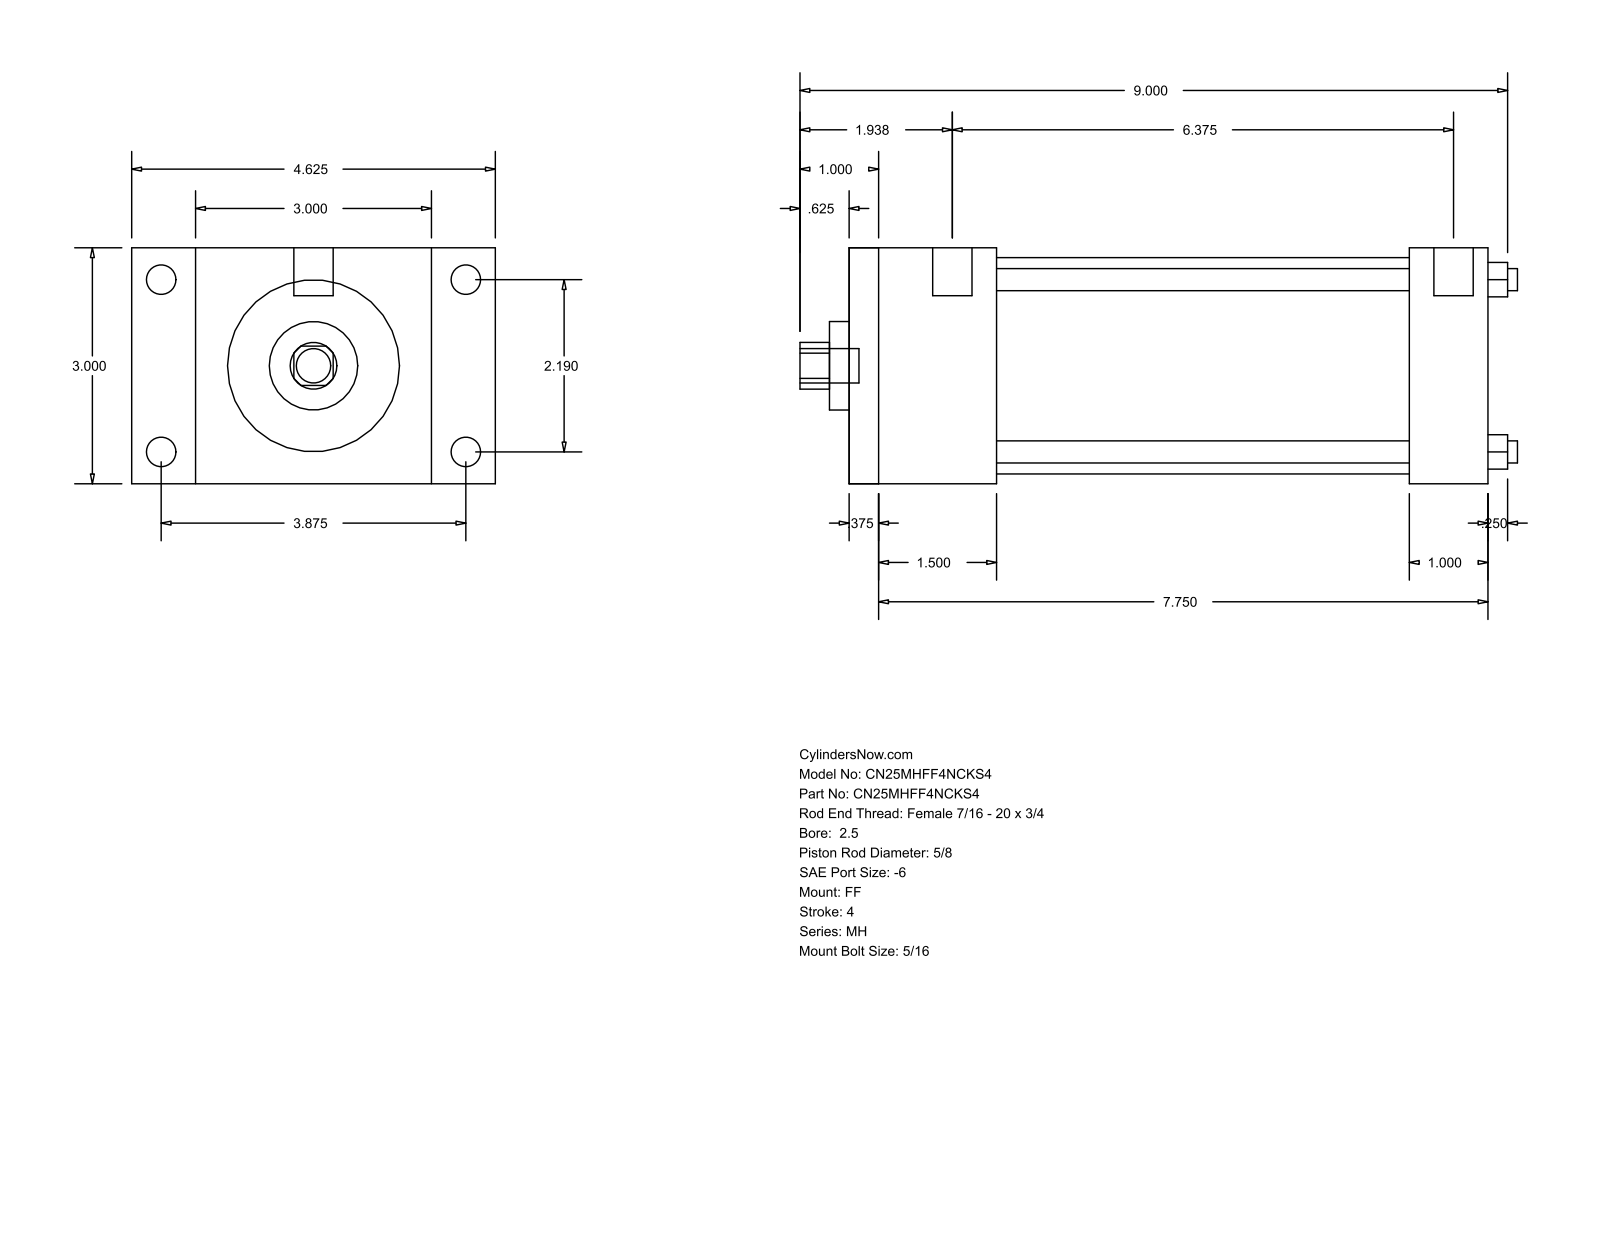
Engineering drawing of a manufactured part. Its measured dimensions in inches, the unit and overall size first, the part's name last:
Units: inches
Overall size (bounding box): 9.125 × 4.625 × 3
Round holes (diameter × count): ⌀0.281 ×4, ⌀0.625 ×1, ⌀1.125 ×1, ⌀2.75 ×1
Round bosses / shafts (diameter × count): ⌀0.375 ×4, ⌀0.219 ×4, ⌀0.5 ×2, ⌀0.437 ×1
Partial cylindrical surfaces — rounded edges, fillets, slot ends (radius × count): R0.297 ×1
Main face-to-face distances: 3, 8.125, 0.375, 7.75, 1, 1.875, 7.125, 1.5, 6.75, 5.25
Hole centre spacings: 1.548, 2.19, 3.097
Bodies: 0 solids, 92 faces (64 planar, 28 cylindrical, 0 other)
Part name (STEP PRODUCT): MH_FF__0250_0.625
STEP written by: GSSL Pune (CONFIG_CONTROL_DESIGN)
